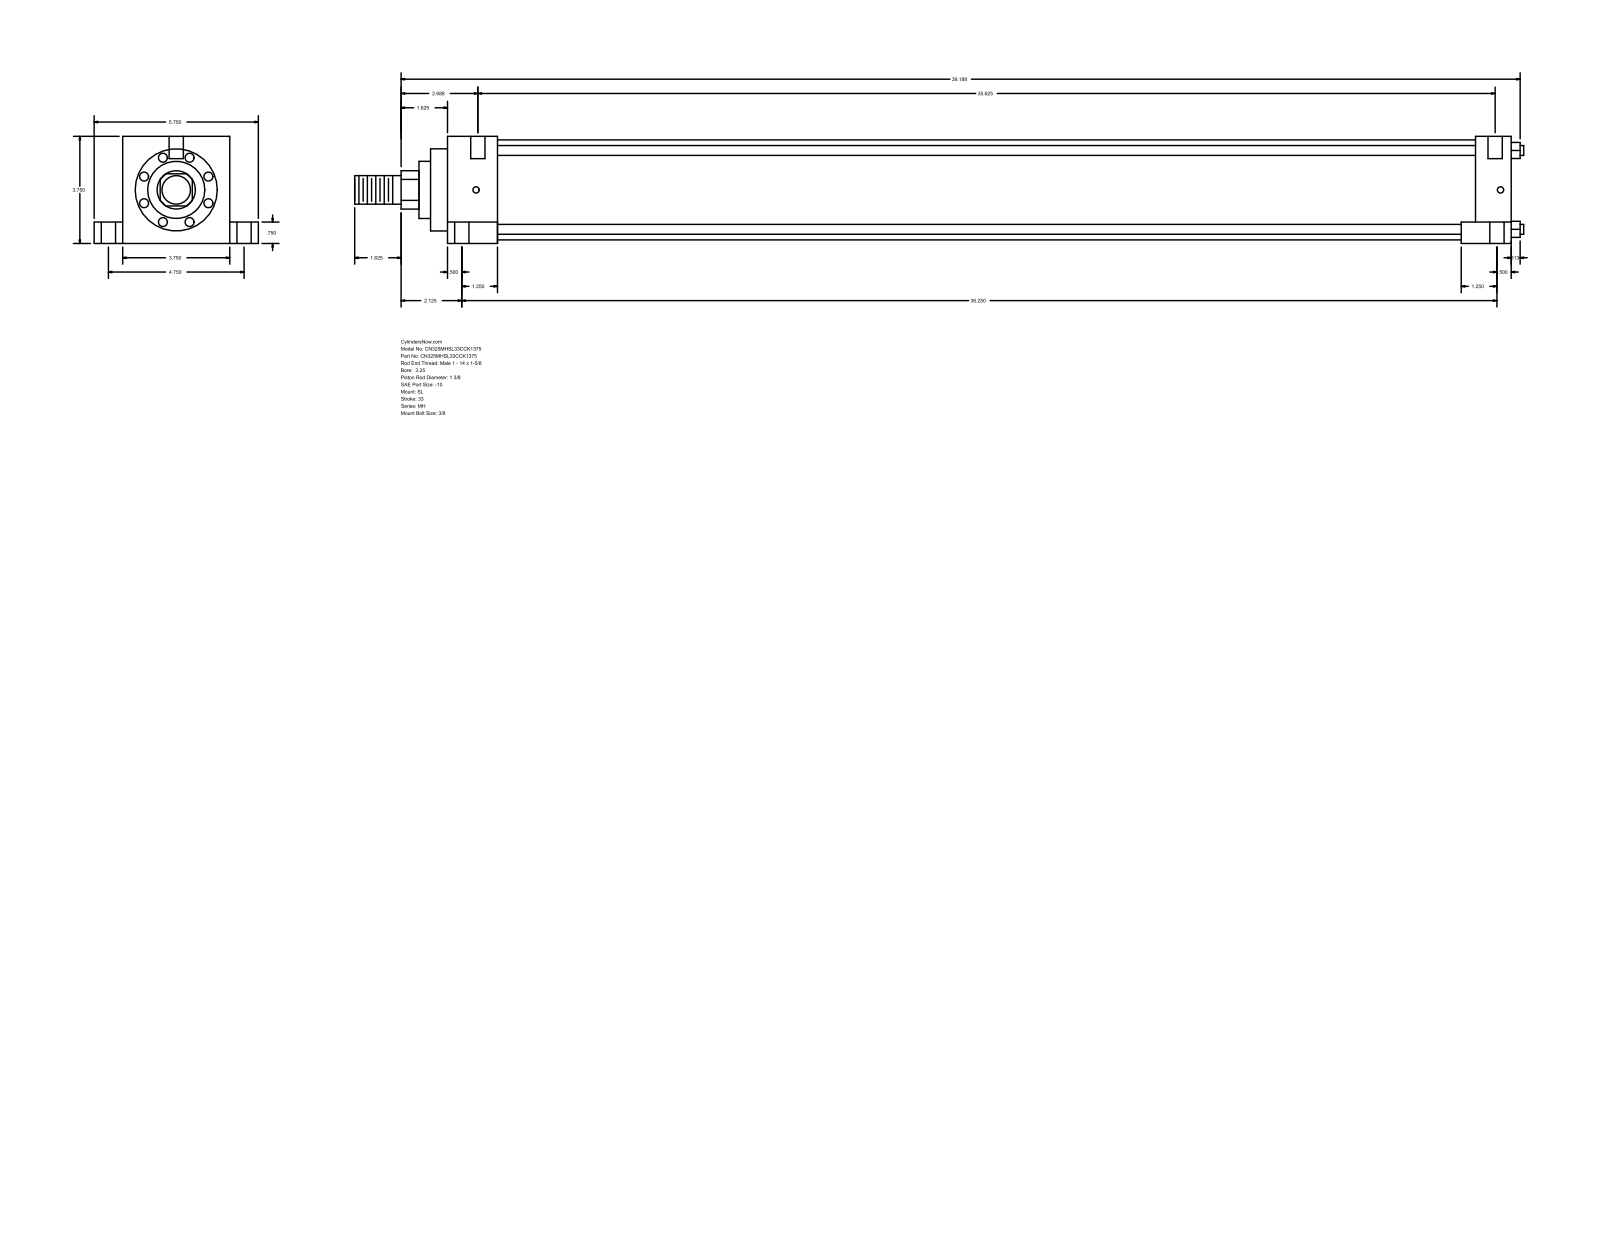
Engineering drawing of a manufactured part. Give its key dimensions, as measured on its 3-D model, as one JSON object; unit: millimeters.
{"part_name": "MH_SL__0325_1.375", "step_written_by": "GSSL Pune (CONFIG_CONTROL_DESIGN)", "units": "millimeters", "bodies": {"solids": 0, "faces": 110, "planar": 77, "cylindrical": 33, "other": 0}, "overall_size": [1039.81, 146.05, 95.25], "round_holes": [[12.7, 6], [5.56, 4], [19.05, 4]], "round_bosses_or_shafts": [[8.76, 4], [88.9, 1], [73.03, 1], [50.8, 1], [34.92, 1], [25.4, 1]], "partial_cylinders_radius": [[17.06, 1]], "face_to_face_distances": [95.24, 946.15, 44.45, 901.7, 25.41, 120.65, 19.05, 76.19, 914.4, 869.95], "hole_center_spacings": [60.35, 60.41, 61.65, 62, 120.66, 908.48, 910.06, 911.23]}
